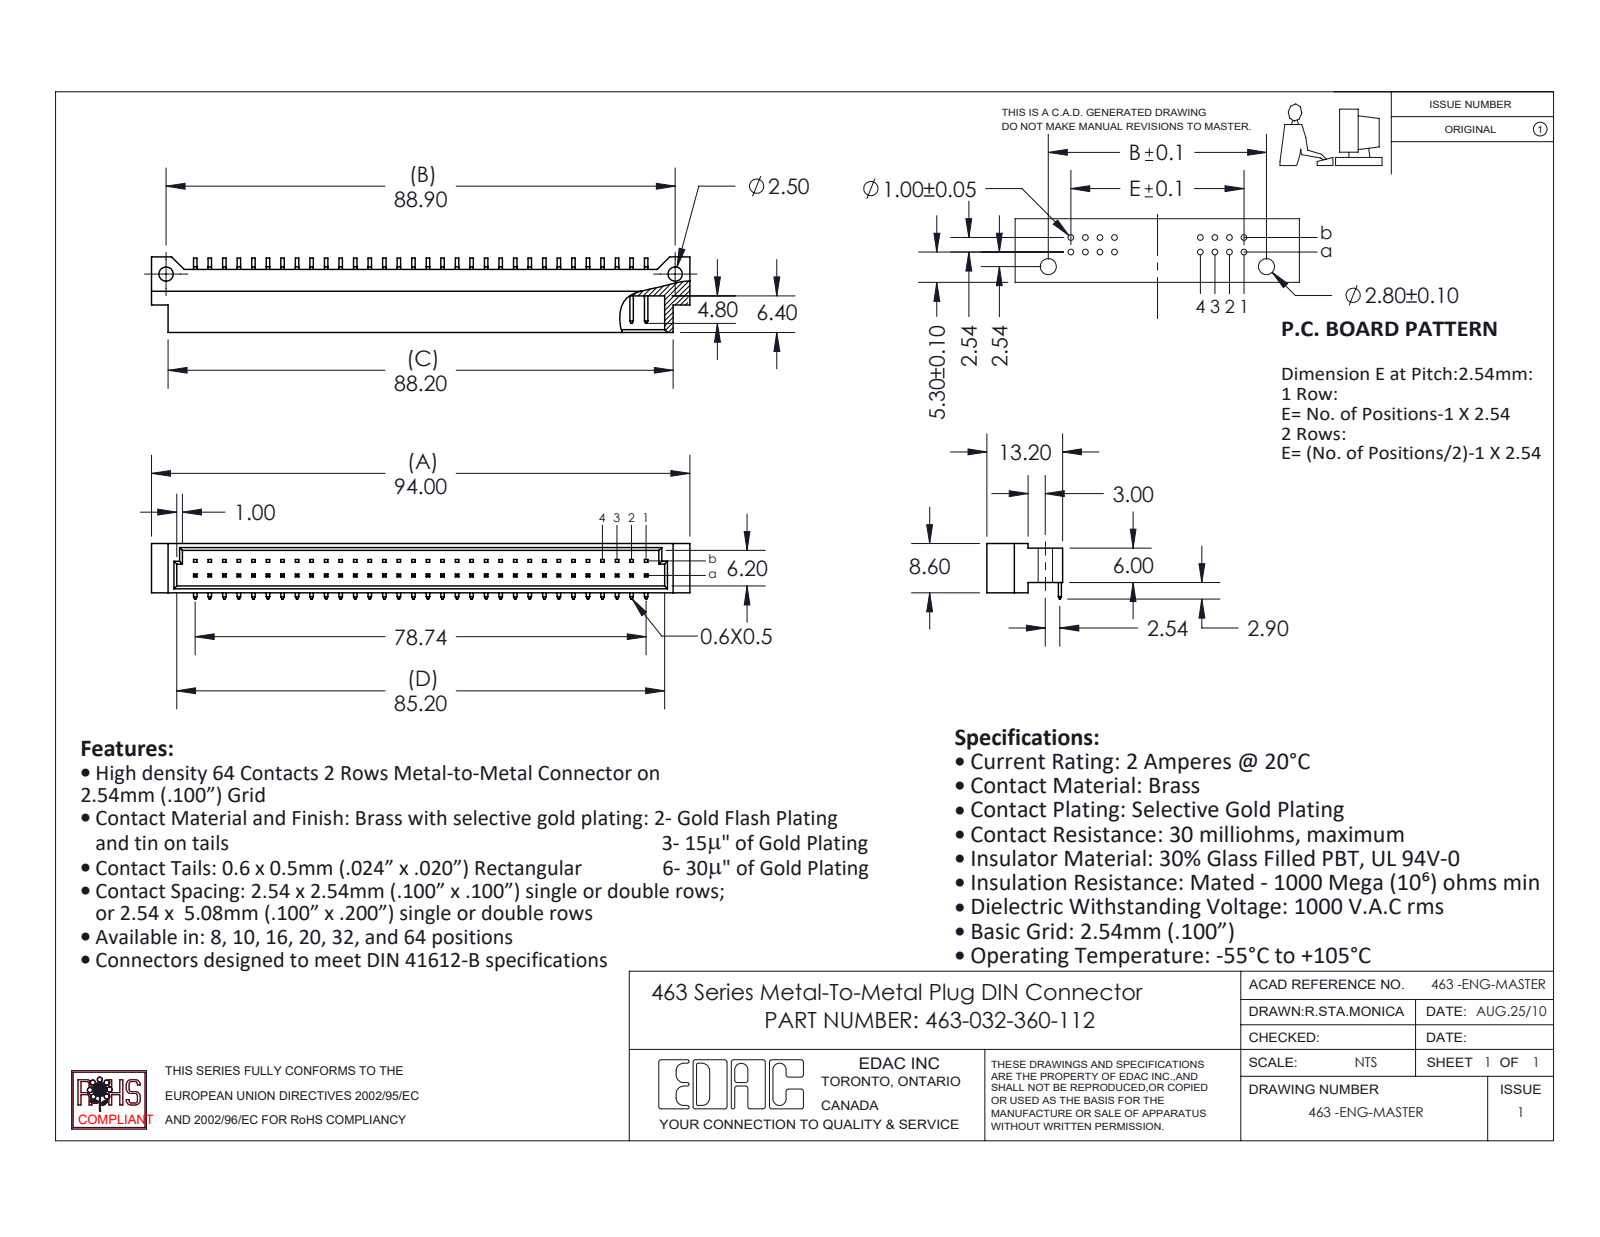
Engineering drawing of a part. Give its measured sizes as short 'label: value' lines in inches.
name: 463-290-1; 463-032-360-112; 463 Part_64
written by: SolidWorks 2020 (CONFIG_CONTROL_DESIGN)
unit: in
bodies: 33 solids, 871 faces (803 planar, 68 cylindrical, 0 other)
size: 3.701 × 0.52 × 0.382
volume: 0.272 in³; area: 10.39 in²
holes: 2× ⌀0.098
rounds: 1× R0.04, 1× R0.06
face distances: 0.047, 0.291, 0.339, 0.031, 0.244, 0.181, 0.236, 0.268, 0.02, 0.22
hole spacings: 3.5
